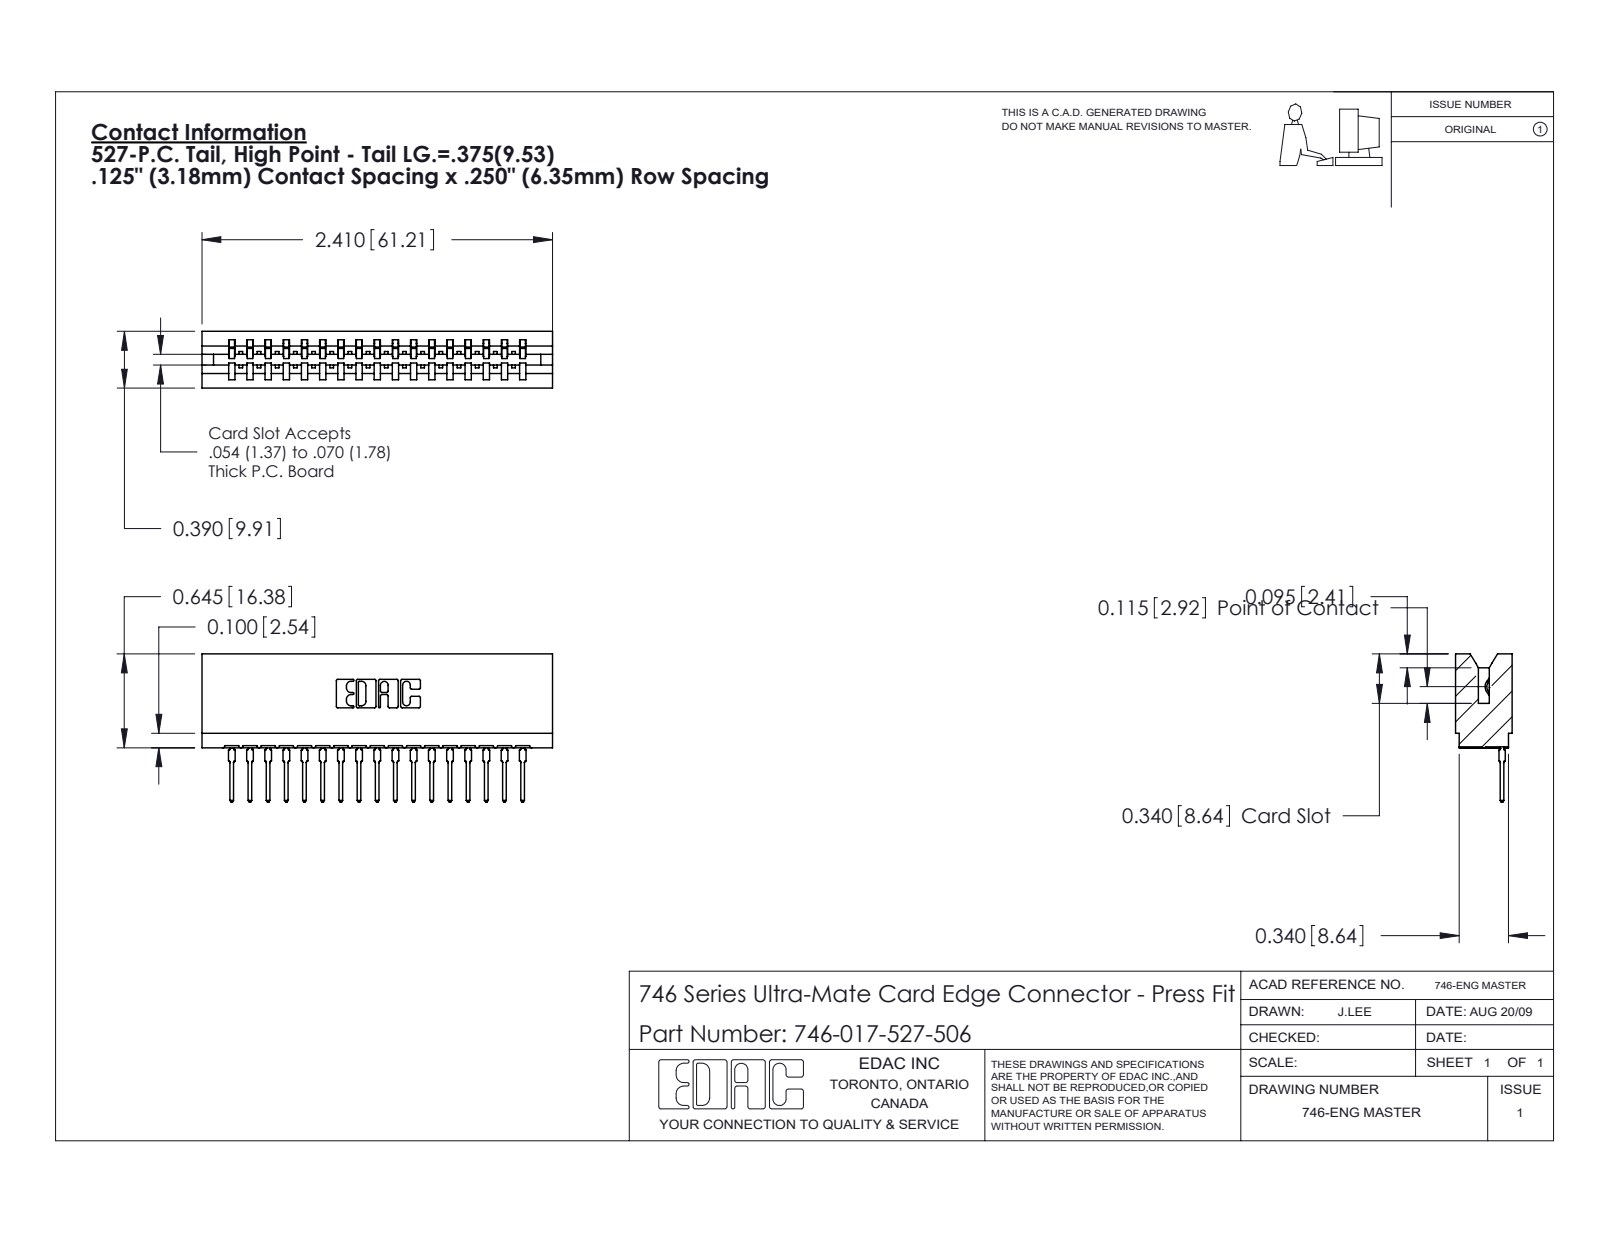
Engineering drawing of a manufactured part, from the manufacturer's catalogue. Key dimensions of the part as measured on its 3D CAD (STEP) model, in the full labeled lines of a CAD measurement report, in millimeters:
Part name (STEP PRODUCT): 746-017-527-506; 746 Part_.340 Slot Depth - 06; 746-292-001_527
STEP written by: SolidWorks 2020 (CONFIG_CONTROL_DESIGN)
Units: millimetres
Bodies: 18 solids, 1934 faces (1127 planar, 365 cylindrical, 442 other)
Overall size (bounding box): 61.2 × 25.9 × 9.9
Volume: 7 010 mm³ · Surface area: 9 194 mm²
Partial cylindrical surfaces — rounded edges, fillets, slot ends (radius × count): R0.5 ×34, R0.3 ×22, R0.4 ×18, R0.2 ×6, R0.8 ×6, R0.1 ×4, R0.3 ×4, R0.7 ×3
Main face-to-face distances: 6.4, 1.4, 8.5, 9.9, 12.7, 3.2, 1.1, 3.2, 0.6, 7.8
